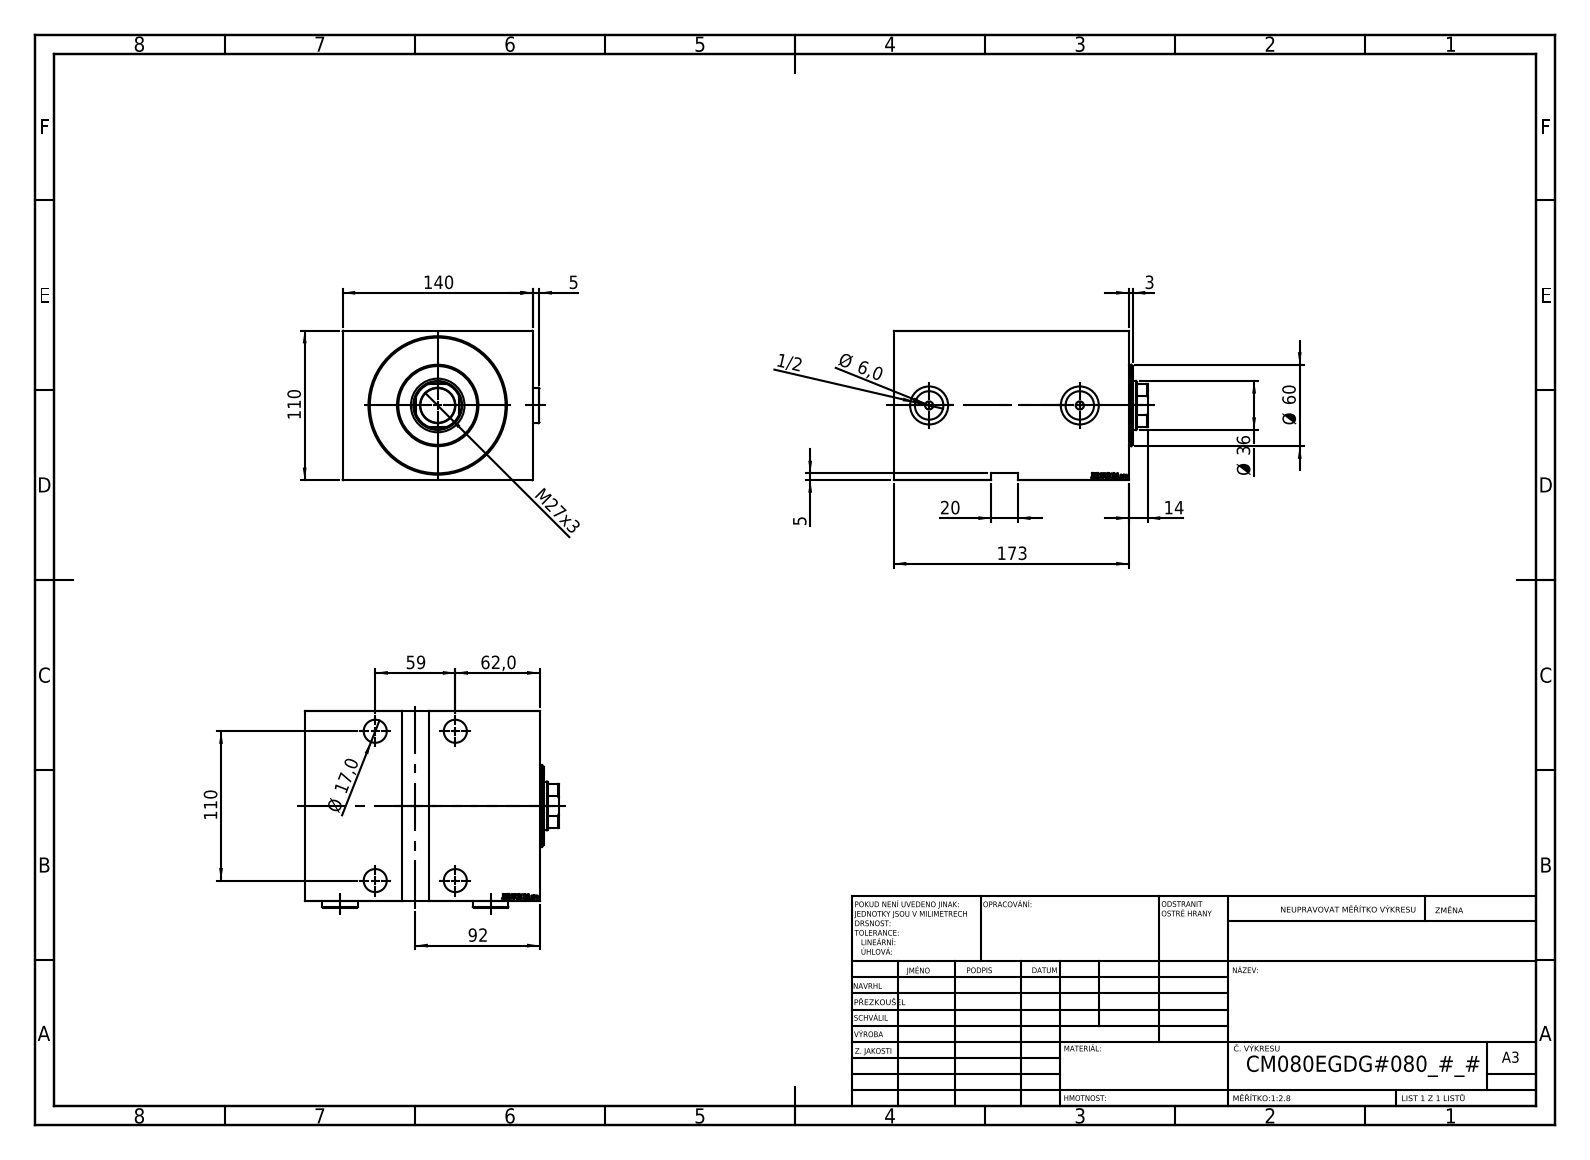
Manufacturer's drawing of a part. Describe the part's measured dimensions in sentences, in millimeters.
The part is named "V450CM_E_Body; V450CM_E_VCP; Zatka_OIL_PORT; V450CM_VC_B". Its 3-D file was written by "SolidWorks 2019 (CONFIG_CONTROL_DESIGN)". It is 5 solids with 912 faces: 446 planar, 68 cylindrical and 398 other. Overall it measures 187 by 144.9 by 110 millimeters. Its volume is 2 201 000 cubic millimeters and its surface area 248 815 square millimeters. Round holes: 4 of diameter 17, 4 of diameter 25, 2 of diameter 6, 2 of diameter 20.96, 2 of diameter 28, 1 of diameter 25.5, 1 of diameter 36, 1 of diameter 39.5, 1 of diameter 80, 1 of diameter 100. Round bosses or shafts: 2 of diameter 26, 1 of diameter 82, 1 of diameter 60. Partial cylindrical surfaces (rounded edges, fillets, slot ends): 1 of radius 17.5. The main face-to-face distances are 110, 140, 173, 21, 152, 5, 168, 147, 79, 156.4. The hole center spacings are 59, 110, 124.82, 111.
